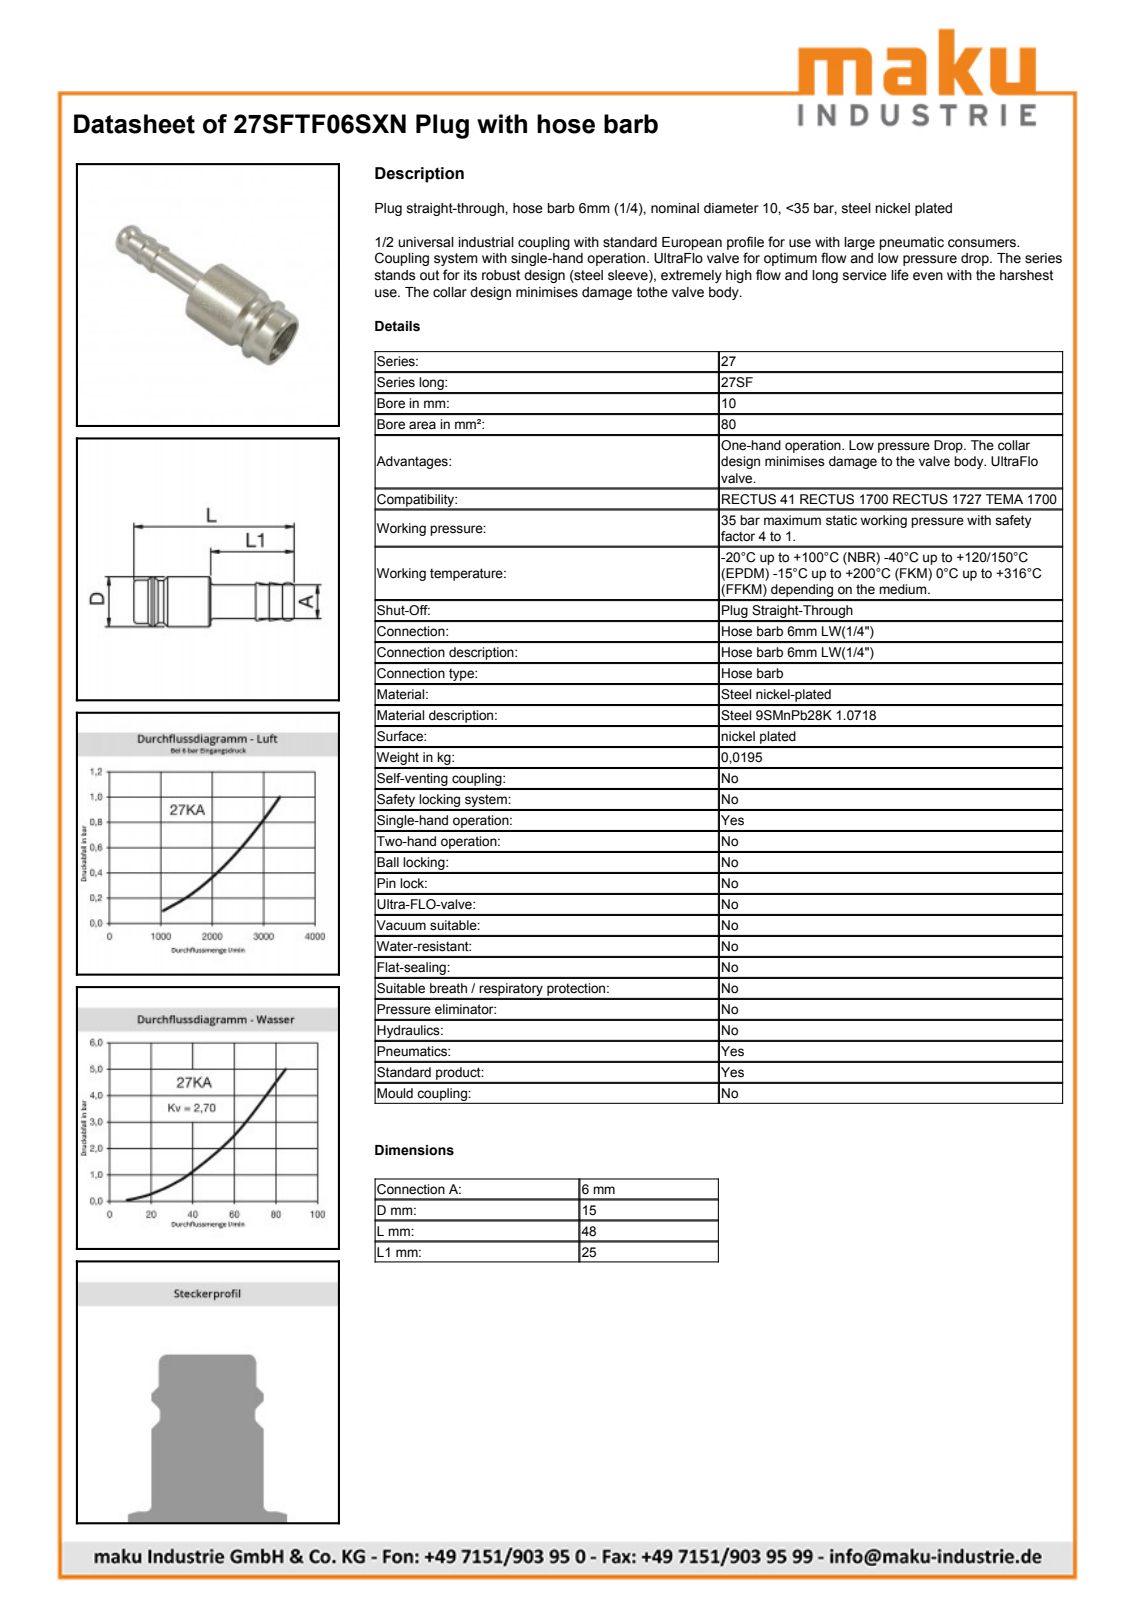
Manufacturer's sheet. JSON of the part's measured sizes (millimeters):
{"part_name": "D103760", "step_written_by": "Autodesk Inventor 2011 (AUTOMOTIVE_DESIGN)", "units": "millimeters", "bodies": {"solids": 1, "faces": 26, "planar": 4, "cylindrical": 7, "other": 15}, "overall_size": [48, 15, 15], "volume_mm3": 2835, "surface_area_mm2": 2784, "round_holes": [[4.1, 1], [9, 1]], "round_bosses_or_shafts": [[15, 1], [13, 1], [12.65, 1], [6.1, 1]], "face_to_face_distances": [23, 48, 25, 36.5, 13.5, 11.5]}
